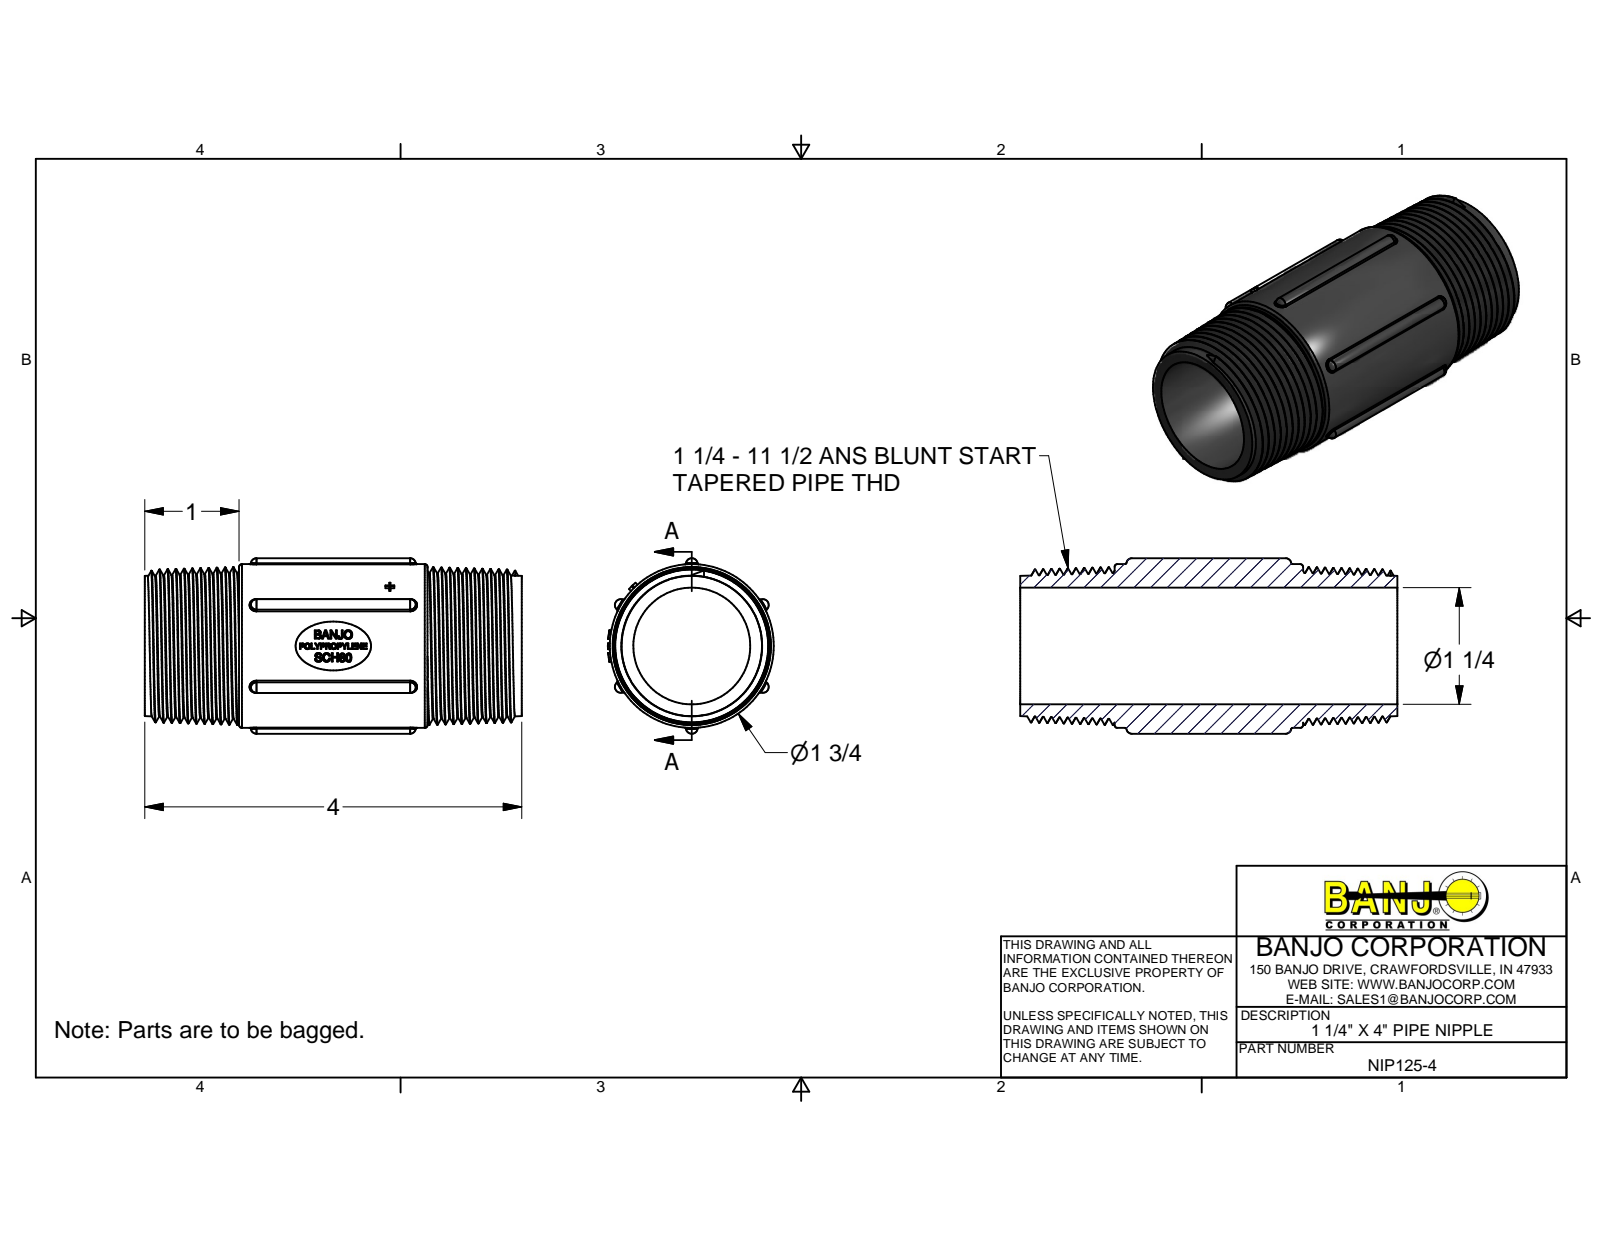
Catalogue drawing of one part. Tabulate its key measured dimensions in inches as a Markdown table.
| quantity | value |
| --- | --- |
| part name | NIP125-4 |
| STEP written by | Autodesk Inventor 2013 (AUTOMOTIVE_DESIGN) |
| units | inches |
| bodies | 1 solid, 424 faces (170 planar, 58 cylindrical, 196 other) |
| overall size | 4 × 1.865 × 1.76 |
| volume | 3.901 in³ |
| surface area | 46.77 in² |
| round holes (diameter × count) | 1.24 × 1 |
| round bosses / shafts (diameter × count) | 1.74 × 1 |
| partial cylindrical surfaces (radius × count) | 0.015 × 12, 0.063 × 6, 0.86 × 1, 0.89 × 1, 0.9 × 1 |
| main face-to-face distances | 4, 1, 3, 2, 0.06, 0.053, 0.046, 0.118, 0.013, 0.015 |
